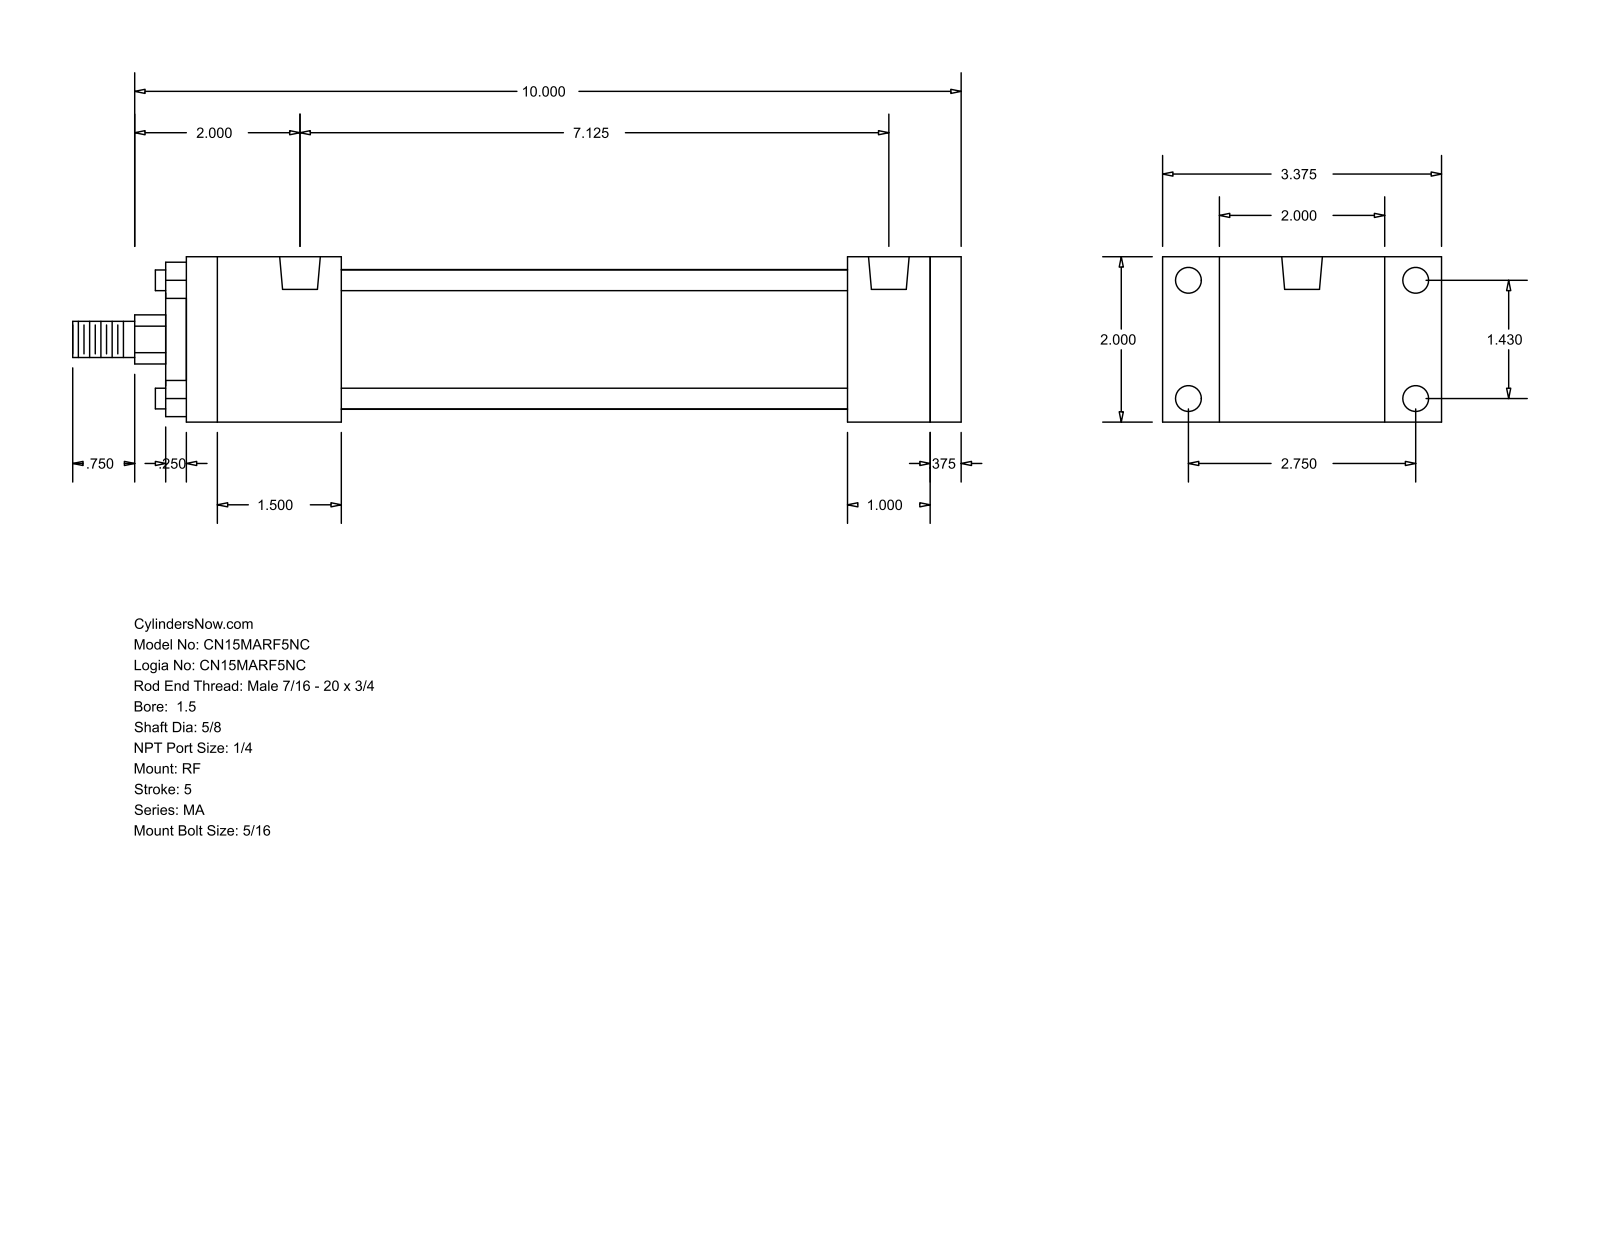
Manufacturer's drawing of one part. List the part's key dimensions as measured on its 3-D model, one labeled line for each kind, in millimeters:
Part name (STEP PRODUCT): MA_RF__0150_0.625
STEP written by: GSSL Pune (CONFIG_CONTROL_DESIGN)
Units: millimetres
Bodies: 0 solids, 92 faces (64 planar, 28 cylindrical, 0 other)
Overall size (bounding box): 273.05 × 85.72 × 50.8
Round holes (diameter × count): ⌀7.94 ×8, ⌀12.49 ×2
Round bosses / shafts (diameter × count): ⌀6.35 ×4, ⌀42.93 ×1, ⌀28.57 ×1, ⌀15.88 ×1, ⌀11.11 ×1
Partial cylindrical surfaces — rounded edges, fillets, slot ends (radius × count): R7.54 ×1
Main face-to-face distances: 50.8, 9.53, 238.12, 228.59, 25.4, 34.93, 203.19, 47.62, 155.57, 180.97
Hole centre spacings: 36.32, 69.84, 78.72, 180.98
